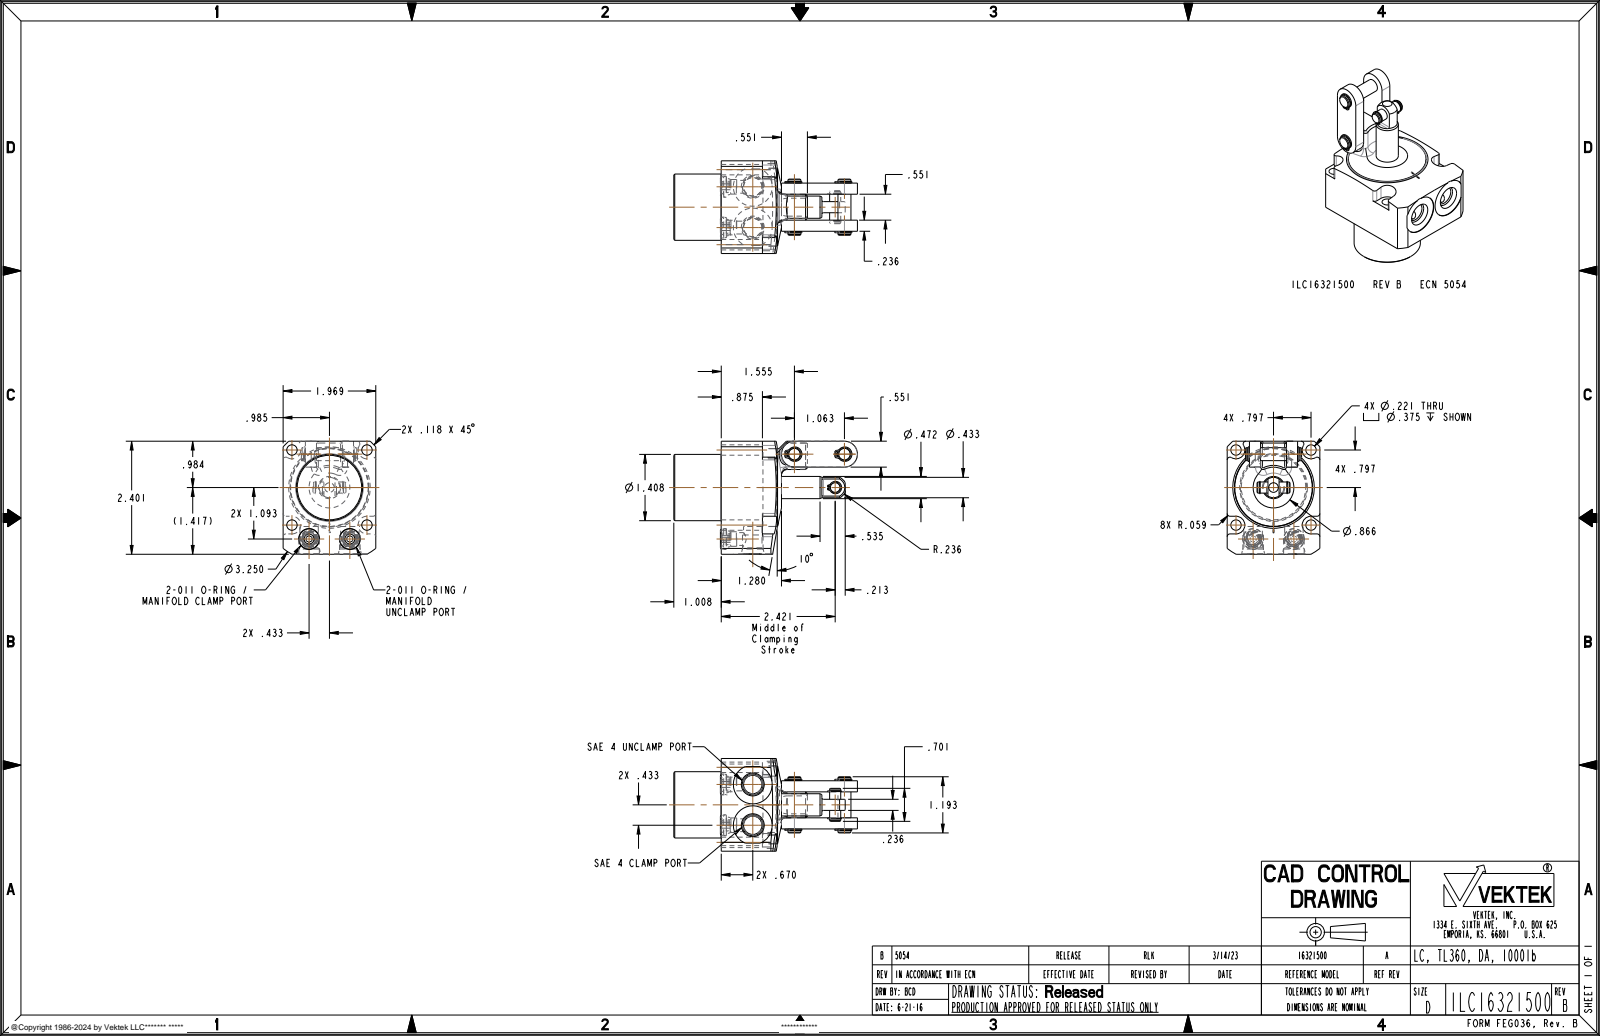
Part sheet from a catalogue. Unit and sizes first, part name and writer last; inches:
Units: inches
Overall size (bounding box): 3.901 × 2.402 × 1.969
Round holes (diameter × count): ⌀0.041 ×4, ⌀0.221 ×4, ⌀0.026 ×2, ⌀0.272 ×2, ⌀0.392 ×2, ⌀0.443 ×2, ⌀0.825 ×2, ⌀1.655 ×1
Round bosses / shafts (diameter × count): ⌀0.236 ×3, ⌀0.437 ×2, ⌀0.43 ×2, ⌀0.31 ×2, ⌀0.276 ×2, ⌀0.255 ×2, ⌀0.21 ×2, ⌀1.651 ×1
Partial cylindrical surfaces — rounded edges, fillets, slot ends (radius × count): R0.059 ×10, R0.031 ×4, R0.041 ×4, R0.084 ×4, R0.187 ×4, R0.026 ×2, R0.042 ×2, R0.154 ×2
Main face-to-face distances: 0.886, 1.969, 1.008, 1.894, 0.473, 1.496, 0.709, 1.26, 0.236, 0.787
Hole centre spacings: 1.127, 1.594, 0.08, 0.469, 0.866, 1.063, 1.066, 1.176
Volume: 7.533 in³ · Surface area: 46.87 in²
Bodies: 2 solids, 382 faces (132 planar, 173 cylindrical, 77 other)
Part name (STEP PRODUCT): ILC16321500_BODY; ILC16321500_LUG; ILC16321500
STEP written by: CREO PARAMETRIC BY PTC INC, 2021164 (AUTOMOTIVE_DESIGN)
